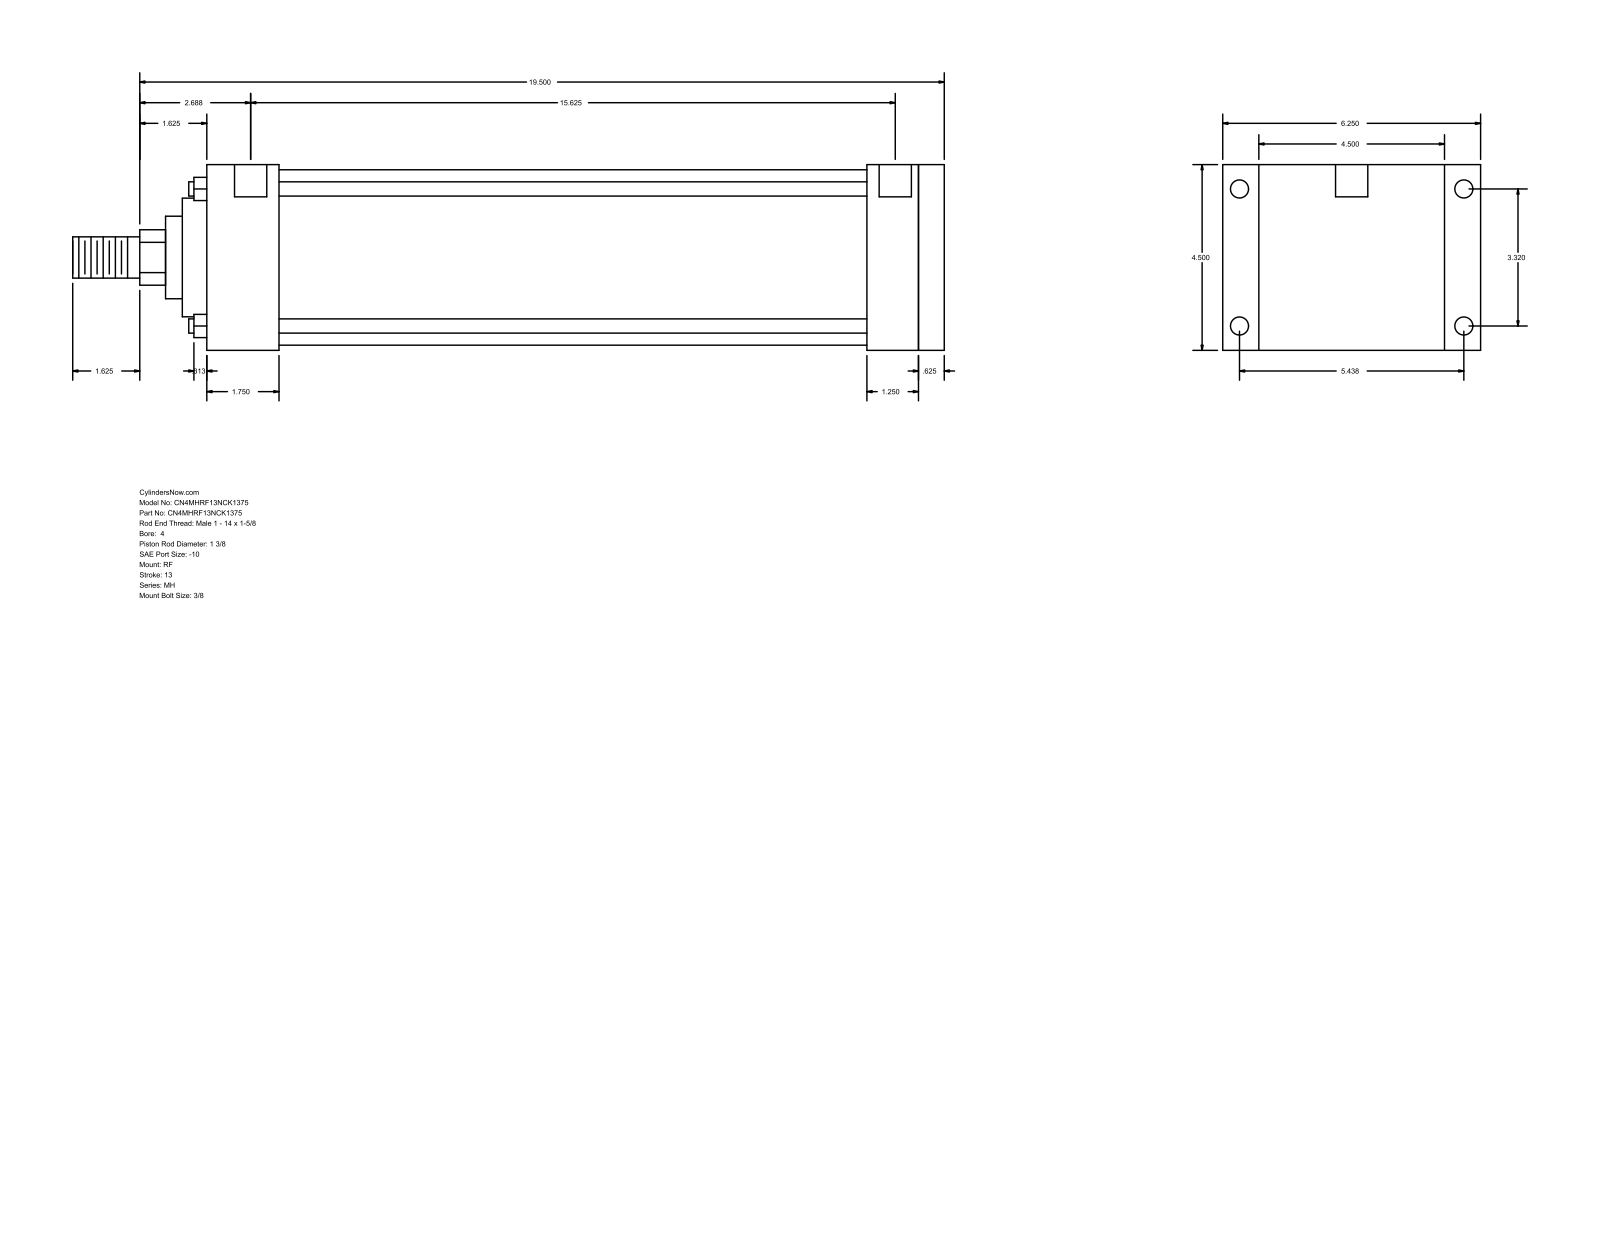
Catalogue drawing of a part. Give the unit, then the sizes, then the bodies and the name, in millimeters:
Units: millimetres
Overall size (bounding box): 536.58 × 158.75 × 114.3
Round holes (diameter × count): ⌀8.73 ×4, ⌀11.13 ×4, ⌀19.84 ×2
Round bosses / shafts (diameter × count): ⌀8.76 ×4, ⌀107.95 ×1, ⌀73.03 ×1, ⌀50.8 ×1, ⌀34.92 ×1, ⌀25.4 ×1
Partial cylindrical surfaces — rounded edges, fillets, slot ends (radius × count): R17.06 ×1
Main face-to-face distances: 114.3, 454.03, 438.16, 15.87, 44.45, 393.71, 409.58, 406.41, 361.96, 31.75
Hole centre spacings: 1.59, 84.32, 138.12, 161.82, 398.47, 400.06, 396.88
Bodies: 0 solids, 94 faces (65 planar, 29 cylindrical, 0 other)
Part name (STEP PRODUCT): MH_RF__0400_1.375
STEP written by: GSSL Pune (CONFIG_CONTROL_DESIGN)
